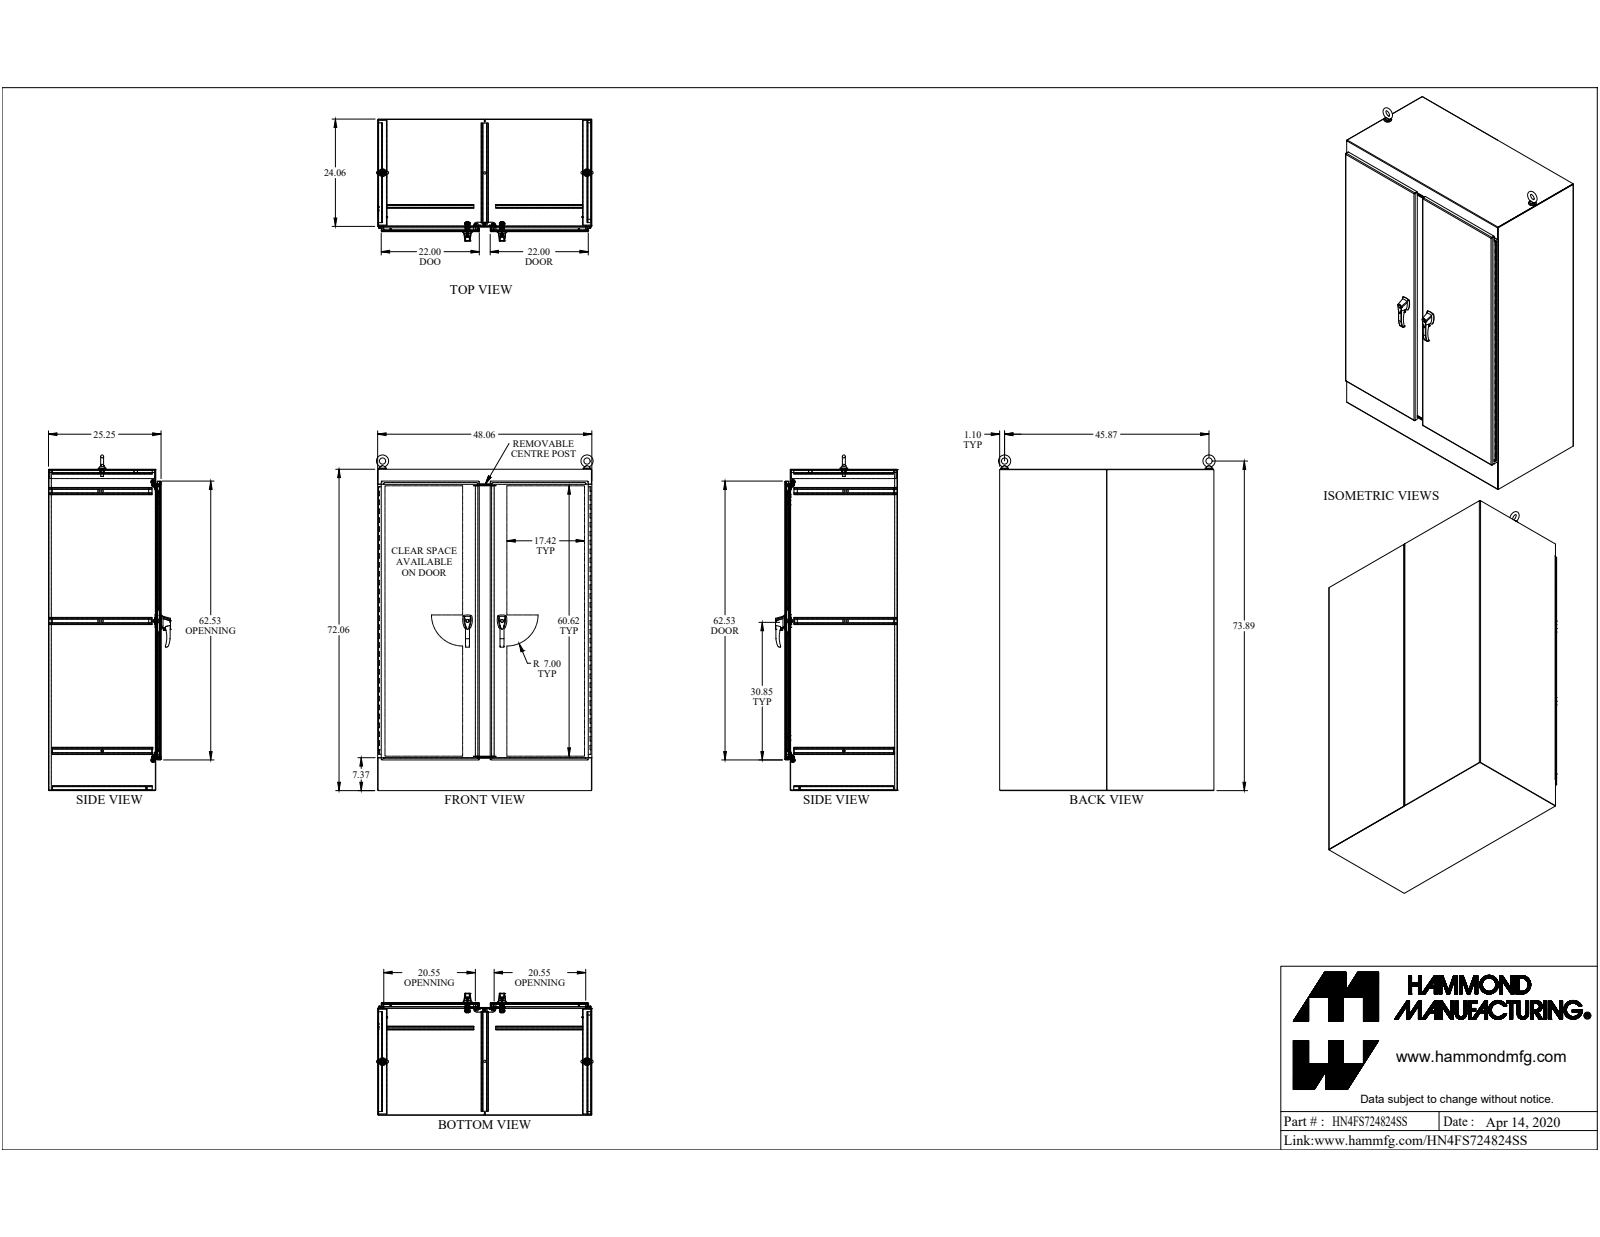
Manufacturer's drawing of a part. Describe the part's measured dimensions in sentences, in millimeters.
The part is named "HN4FS724824SS". Its 3-D file was written by "SolidWorks 2019 (CONFIG_CONTROL_DESIGN)". It is 106 solids with 2965 faces: 1563 planar, 1156 cylindrical and 246 other. Overall it measures 1911.5 by 1234.5 by 695 millimeters. Its volume is 24 760 000 cubic millimeters and its surface area 20 540 000 square millimeters. Round holes: 20 of diameter 7.7, 8 of diameter 8.9, 7 of diameter 6.4, 7 of diameter 12.7, 4 of diameter 6.5, 4 of diameter 7.1, 4 of diameter 7.1, 4 of diameter 8, 4 of diameter 9.9, 4 of diameter 10.5, 3 of diameter 5.1, 3 of diameter 8. Round bosses or shafts: 4 of diameter 25.4, 4 of diameter 19.1, 4 of diameter 16, 4 of diameter 15.9, 4 of diameter 11.2, 4 of diameter 9.4, 4 of diameter 8, 4 of diameter 6.4. Partial cylindrical surfaces (rounded edges, fillets, slot ends): 54 of radius 1.1, 48 of radius 3.5, 33 of radius 12.7, 28 of radius 2.5, 27 of radius 3.2, 24 of radius 0.5, 24 of radius 1.5, 18 of radius 8.1. The main face-to-face distances are 2.4, 638.9, 1218.3, 636.4, 641.3, 1827.9, 1215.9, 1220.7, 30.1, 608.7. The hole center spacings are 152.4, 1186.6, 304.8, 1215.6, 457.2, 1262.4, 609.6, 1325.3.
